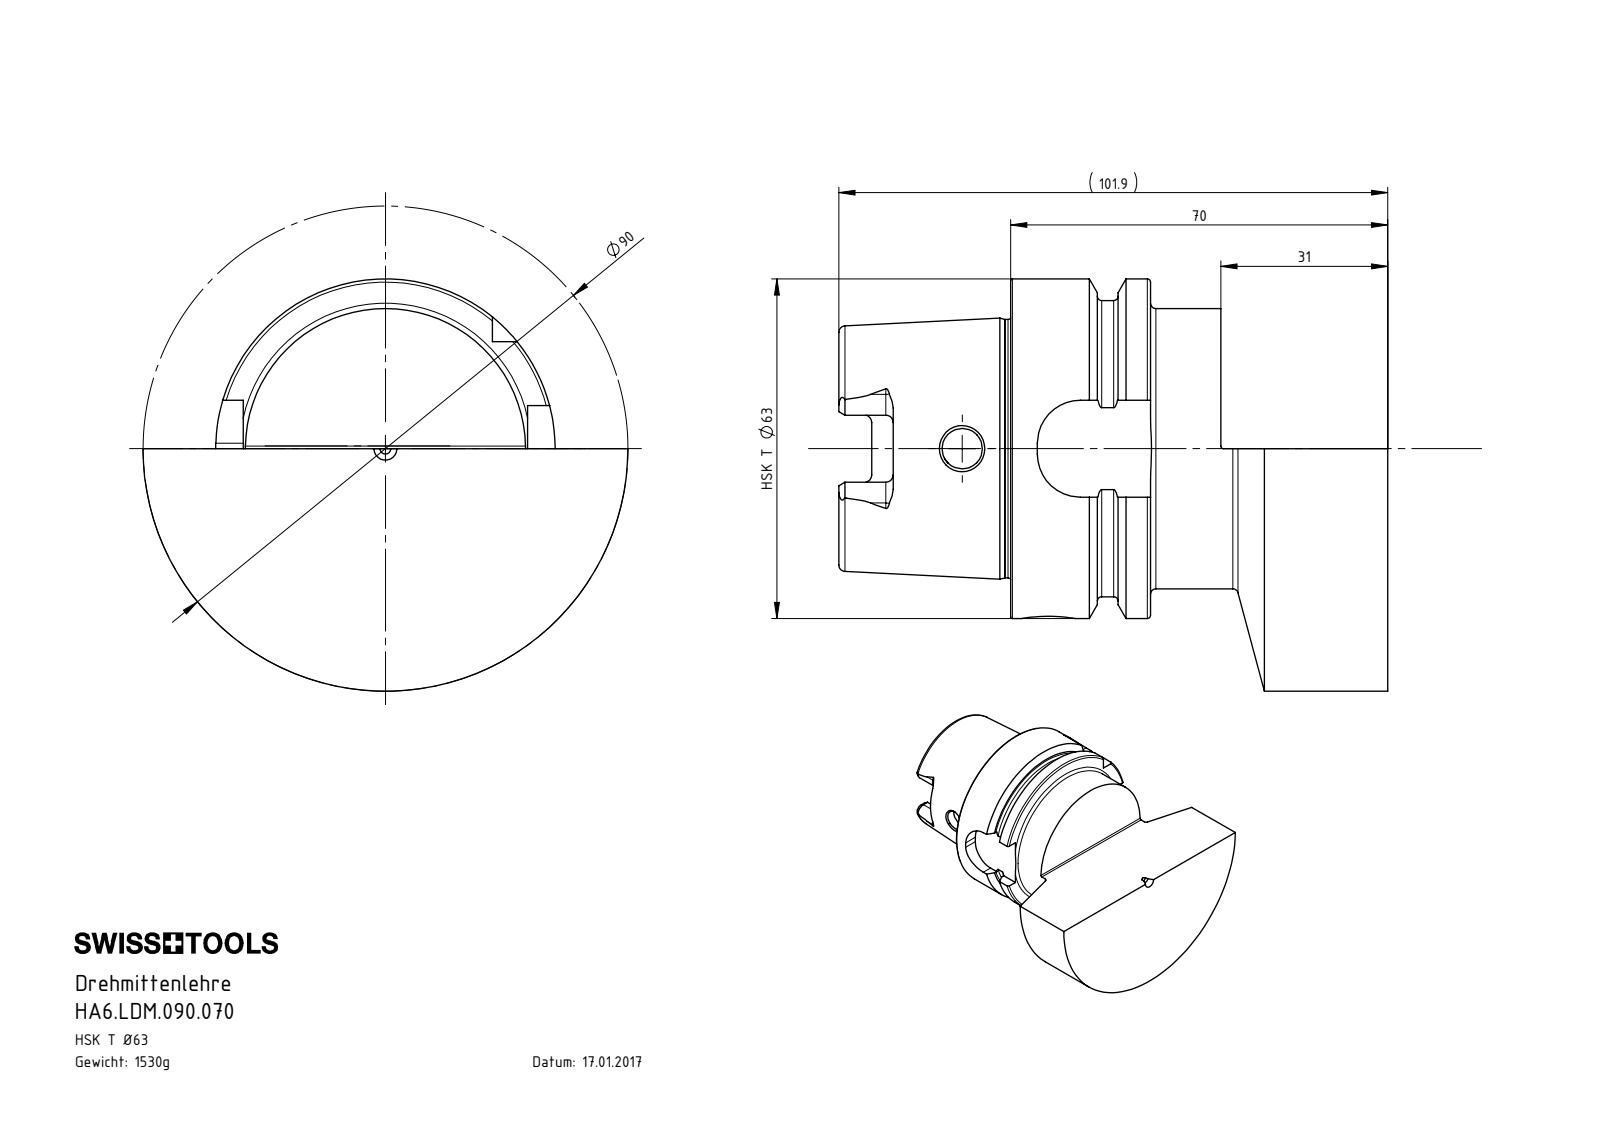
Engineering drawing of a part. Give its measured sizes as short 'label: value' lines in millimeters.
name: HA6-LDM.090.070_A
written by: SolidWorks 2015 (AUTOMOTIVE_DESIGN)
unit: mm
bodies: 1 solid, 158 faces (45 planar, 48 cylindrical, 65 other)
size: 101.9 × 90 × 76.5
volume: 194 961 mm³; area: 34 942 mm²
holes: 1× ⌀7.5, 1× ⌀8.4, 1× ⌀10, 1× ⌀17, 1× ⌀19, 1× ⌀34, 1× ⌀40
bosses: 1× ⌀63, 1× ⌀54.95, 1× ⌀52, 1× ⌀47.94
rounds: 6× R1.4, 4× R2.88, 4× R8, 1× R0.5, 1× R1, 1× R45
face distances: 70, 39, 31, 25.95, 13.05, 44.05, 16, 9.95, 29.05, 60.05
